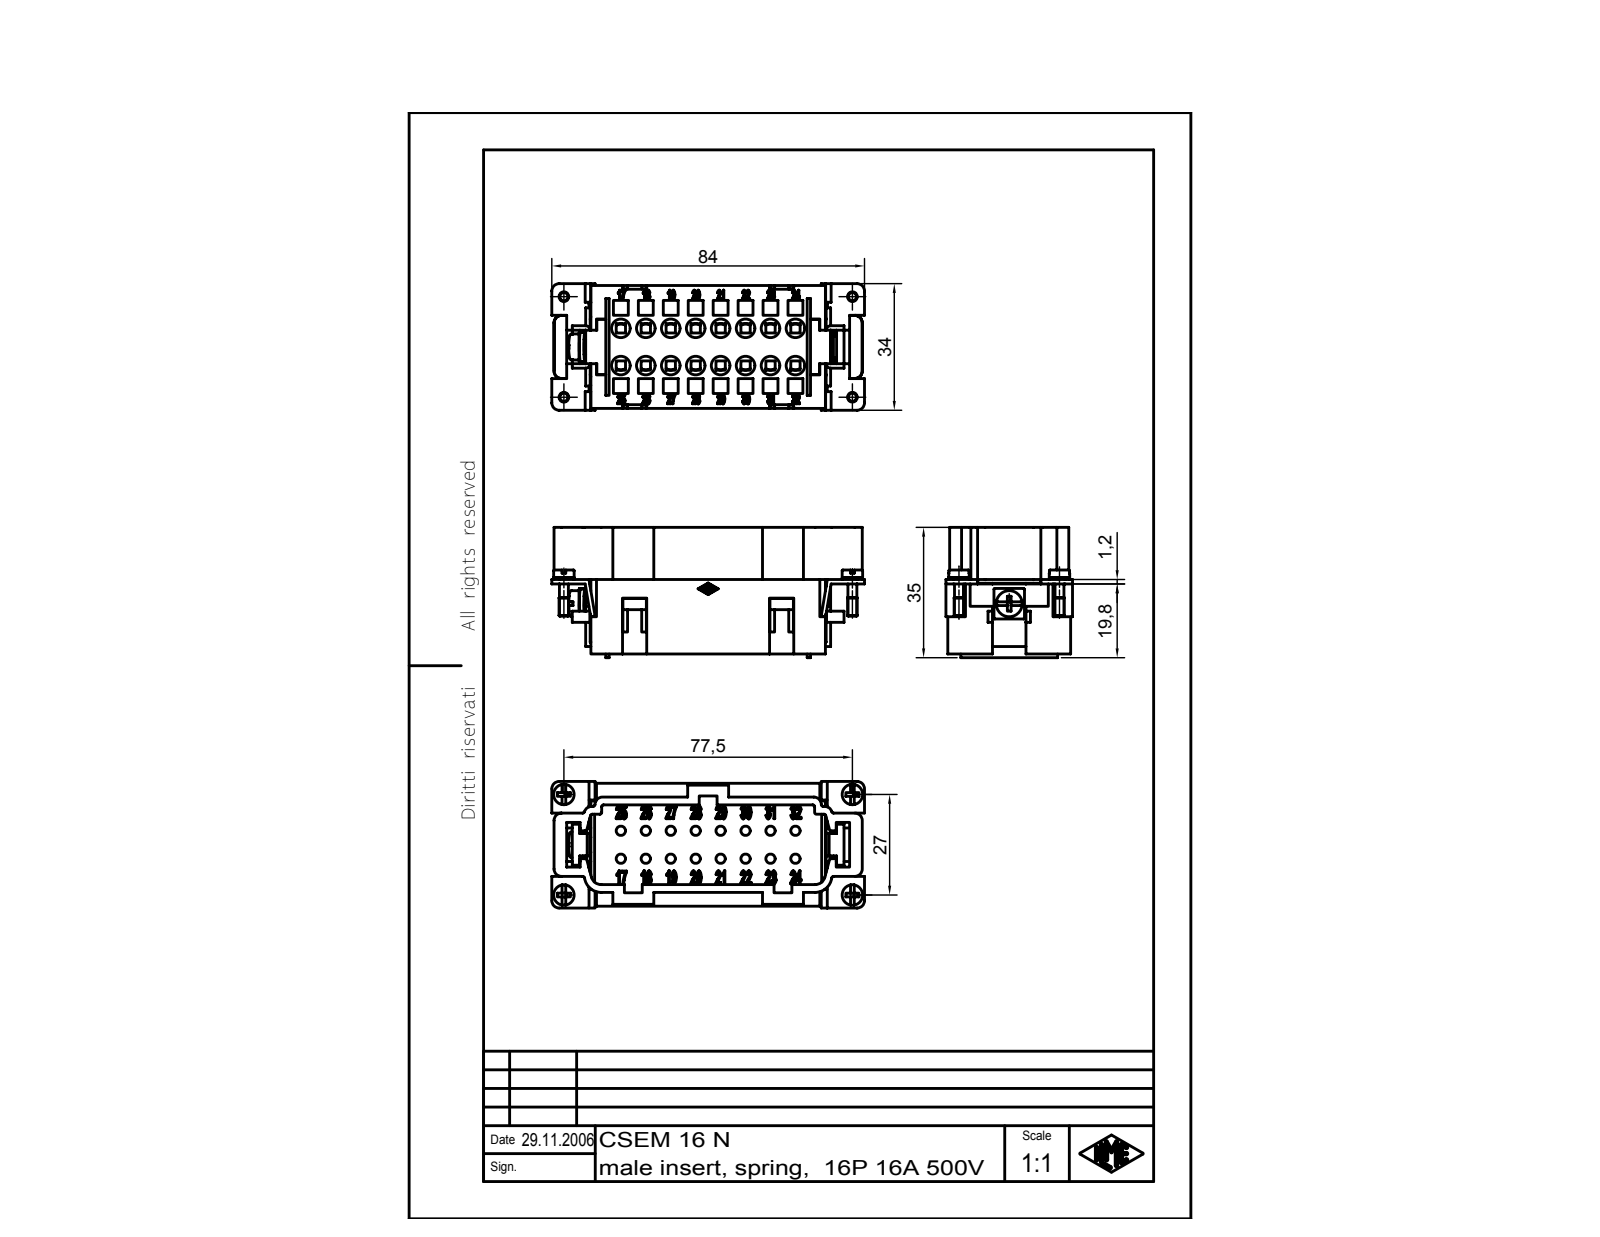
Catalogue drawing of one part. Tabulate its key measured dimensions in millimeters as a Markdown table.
| quantity | value |
| --- | --- |
| part name | CSEM Kontakteinsätze mit Käfigzugfederanschluss |
| STEP written by | Autodesk Inventor 7 (AUTOMOTIVE_DESIGN) |
| units | millimeters |
| bodies | 1 solid, 1835 faces (688 planar, 156 cylindrical, 991 other) |
| overall size | 84 × 35 × 34 |
| volume | 47 983 mm³ |
| surface area | 24 912 mm² |
| round holes (diameter × count) | 5 × 8, 3.24 × 1 |
| round bosses / shafts (diameter × count) | 2.5 × 16, 5.5 × 2, 5.4 × 2, 2.6 × 2, 2.4 × 2, 7 × 1, 4 × 1 |
| partial cylindrical surfaces (radius × count) | 2.4 × 16, 0.1 × 14, 2 × 10, 0.5 × 6, 1.25 × 2, 0.2 × 1, 1.2 × 1, 1.36 × 1 |
| main face-to-face distances | 20, 5.8, 27.2, 2.1, 3.7, 29.3, 23.5, 33, 21.4, 4 |
| hole center spacings | 6.7, 13.4, 20.1, 26.8, 33.5, 40.2, 46.9 |
